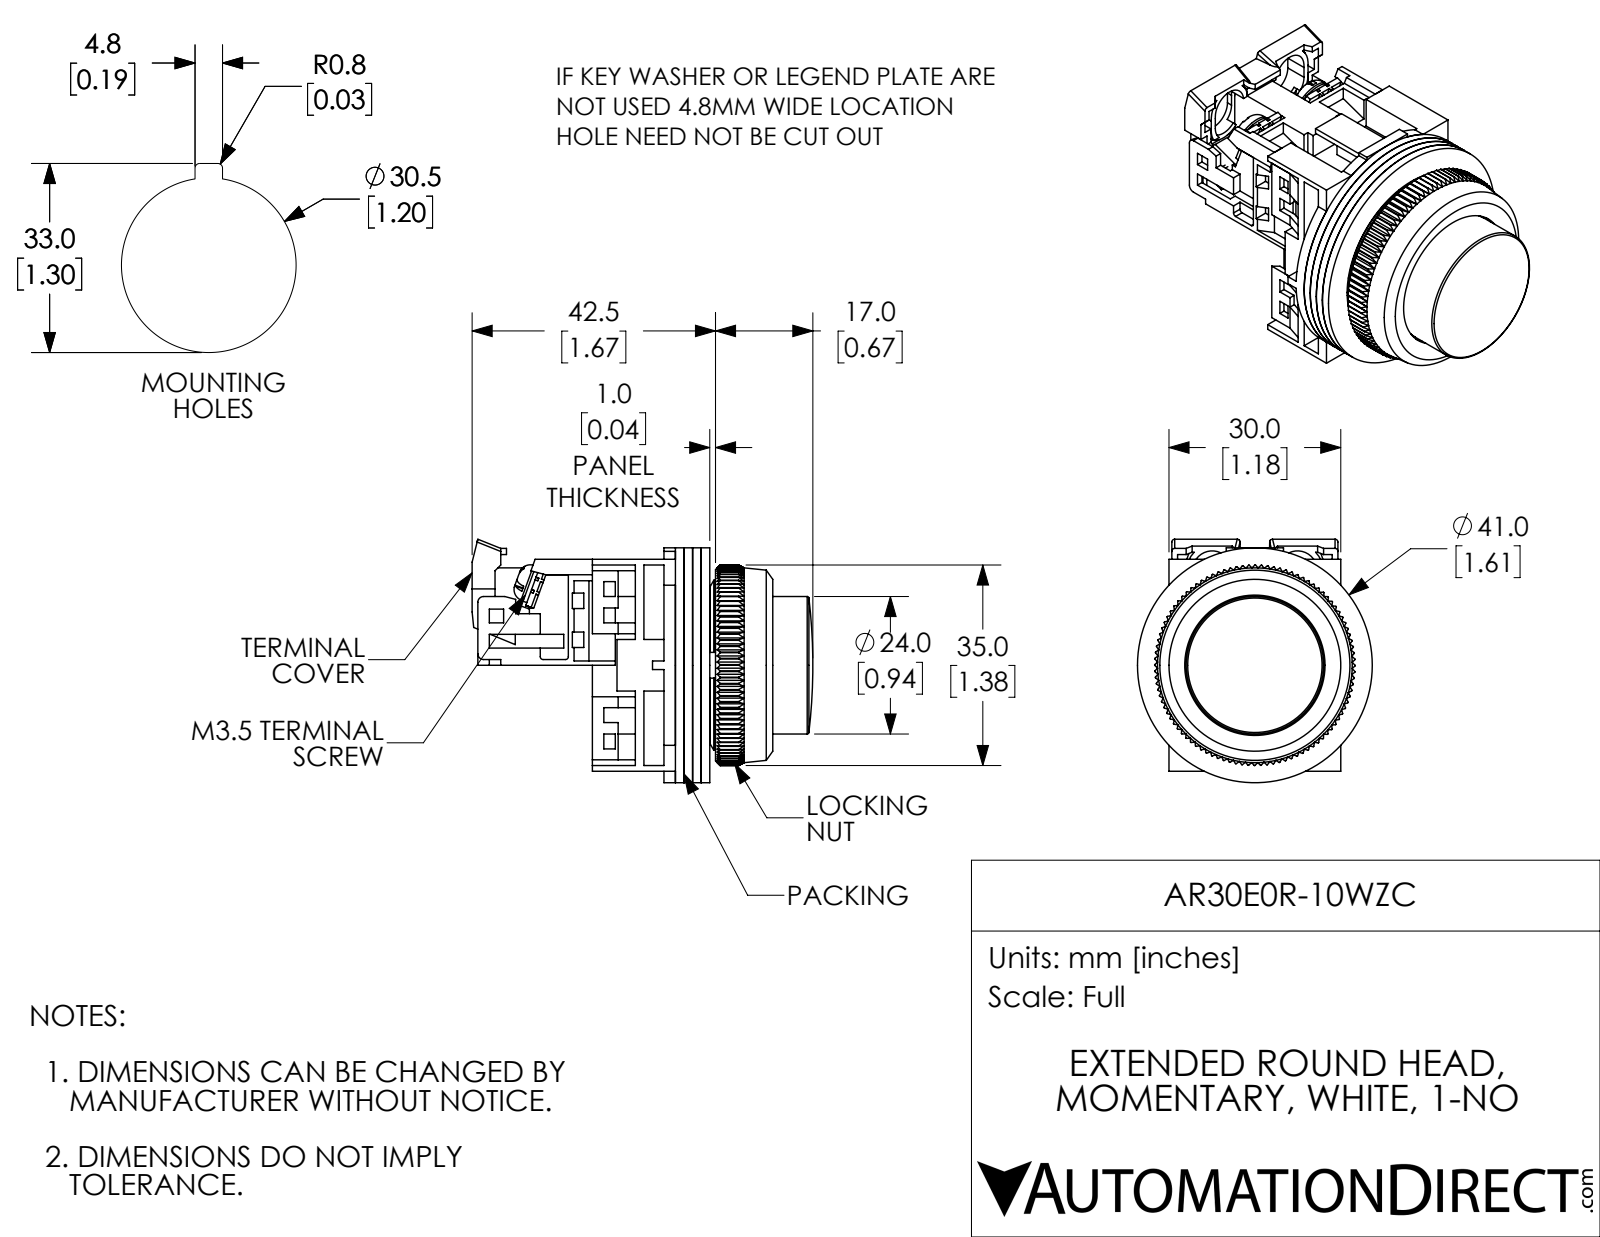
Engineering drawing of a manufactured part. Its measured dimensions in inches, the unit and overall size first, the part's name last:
Units: inches
Overall size (bounding box): 2.342 × 1.673 × 1.614
Round holes (diameter × count): ⌀0.138 ×4, ⌀0.142 ×2, ⌀0.118 ×1, ⌀0.472 ×1, ⌀0.709 ×1, ⌀0.787 ×1, ⌀0.945 ×1, ⌀0.965 ×1, ⌀1.122 ×1, ⌀1.252 ×1
Round bosses / shafts (diameter × count): ⌀0.26 ×2, ⌀0.138 ×2, ⌀1.614 ×1, ⌀1.181 ×1, ⌀0.866 ×1, ⌀0.551 ×1
Partial cylindrical surfaces — rounded edges, fillets, slot ends (radius × count): R0.059 ×8, R0.02 ×6, R0.039 ×2, R0.138 ×2, R0.177 ×2, R0.118 ×1, R0.398 ×1, R0.449 ×1
Main face-to-face distances: 0.059, 0.118, 0.177, 0.039, 0.197, 0.079, 0.276, 0.689, 0.728, 0.602
Hole centre spacings: 0.579, 0.61
Volume: 1.642 in³ · Surface area: 48.85 in²
Bodies: 16 solids, 1234 faces (775 planar, 249 cylindrical, 210 other)
Part name (STEP PRODUCT): AR30E0R-10WZC
STEP written by: SolidWorks 2017 (AUTOMOTIVE_DESIGN)
